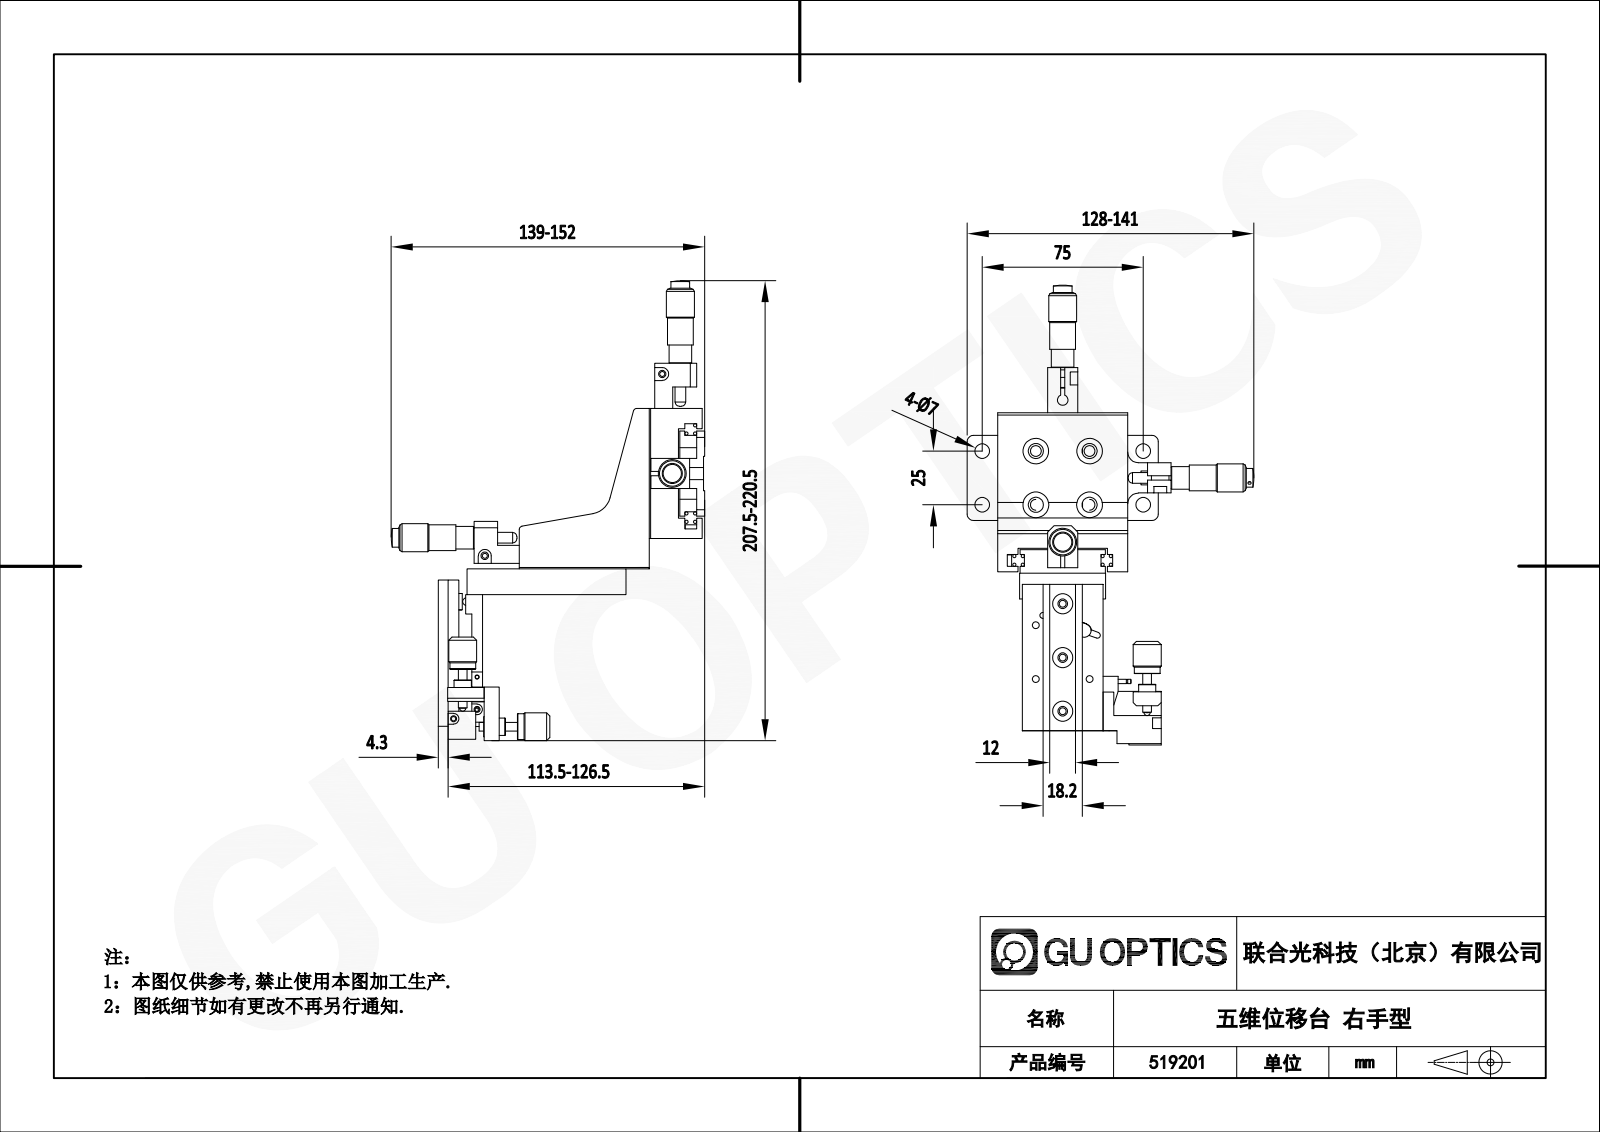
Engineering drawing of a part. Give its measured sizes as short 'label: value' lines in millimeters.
name: FP-XYZT
written by: SolidWorks 2010 (CONFIG_CONTROL_DESIGN)
unit: mm
bodies: 0 solids, 729 faces (320 planar, 339 cylindrical, 70 other)
size: 214 × 145.8 × 133.4
holes: 24× ⌀2, 9× ⌀5, 9× ⌀12, 6× ⌀2.5, 6× ⌀3.3, 4× ⌀7, 3× ⌀1.5, 3× ⌀2.8, 3× ⌀4, 3× ⌀4.5, 3× ⌀6, 3× ⌀10.7
bosses: 24× ⌀1.5, 5× ⌀13, 5× ⌀12, 4× ⌀9.5, 3× ⌀10.5, 3× ⌀8.7, 3× ⌀5, 3× ⌀4
rounds: 8× R3, 4× R1.4, 3× R3.25, 2× R1.5, 2× R2.5, 2× R5, 1× R2, 1× R4
face distances: 11, 0.65, 11.65, 5, 13.65, 2, 60.5, 93.55, 1, 6
hole spacings: 25, 34.59, 4, 16.78, 18.55, 33.66, 35.99, 38.2
